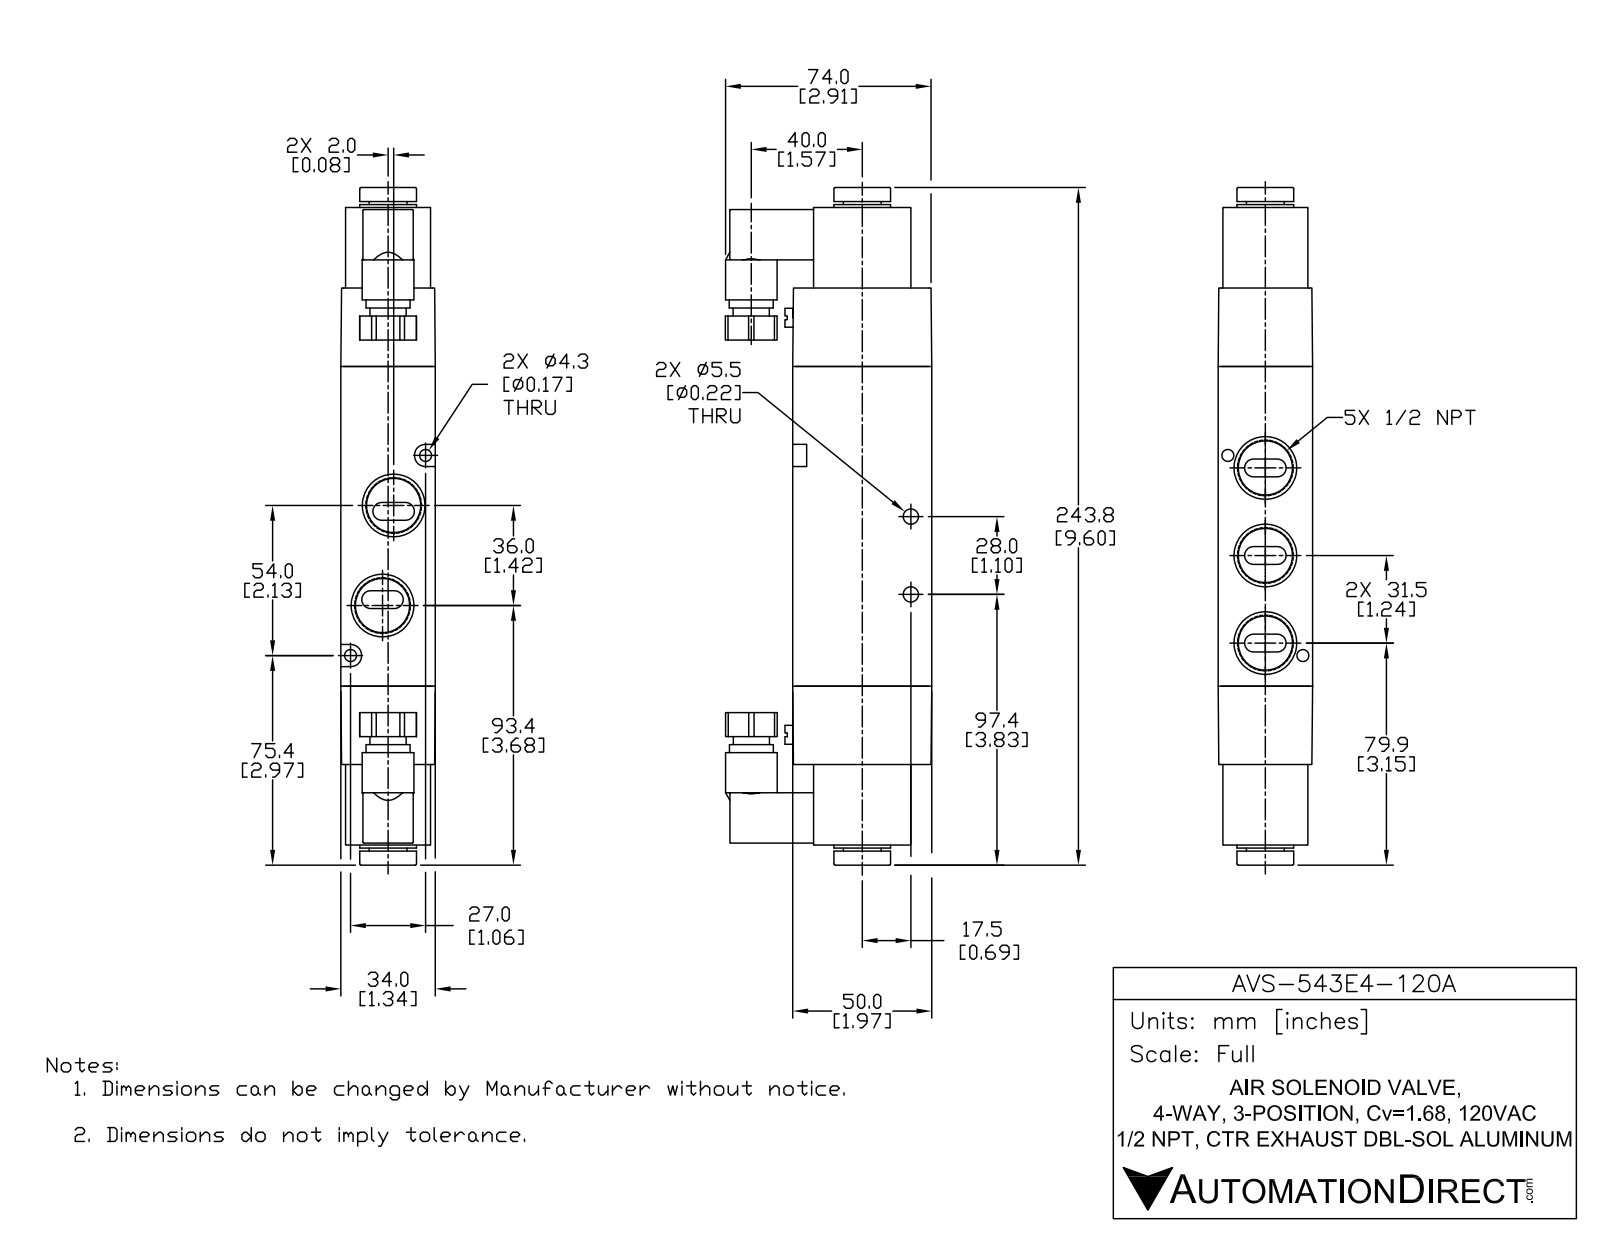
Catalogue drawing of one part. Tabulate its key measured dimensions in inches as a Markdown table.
| quantity | value |
| --- | --- |
| part name | AVS-543E4-120A |
| STEP written by | SolidWorks 2015 (CONFIG_CONTROL_DESIGN) |
| units | inches |
| bodies | 5 solids, 248 faces (111 planar, 103 cylindrical, 34 other) |
| overall size | 9.598 × 2.921 × 1.339 |
| volume | 21.74 in³ |
| surface area | 100 in² |
| round holes (diameter × count) | 0.703 × 5, 0.169 × 2, 0.217 × 2, 0.366 × 1 |
| round bosses / shafts (diameter × count) | 0.264 × 2, 0.819 × 1, 0.803 × 1, 0.732 × 1, 0.622 × 1, 0.535 × 1, 0.512 × 1 |
| partial cylindrical surfaces (radius × count) | 0.059 × 18, 0.039 × 10, 0.126 × 10, 0.157 × 2 |
| main face-to-face distances | 1.339, 4.528, 1.969, 1.416, 1.11, 1.265, 2.046, 0.313, 1.026, 0.713 |
| hole center spacings | 0.537, 0.56, 0.713, 0.841, 1.24, 1.514, 1.95, 2.212 |
